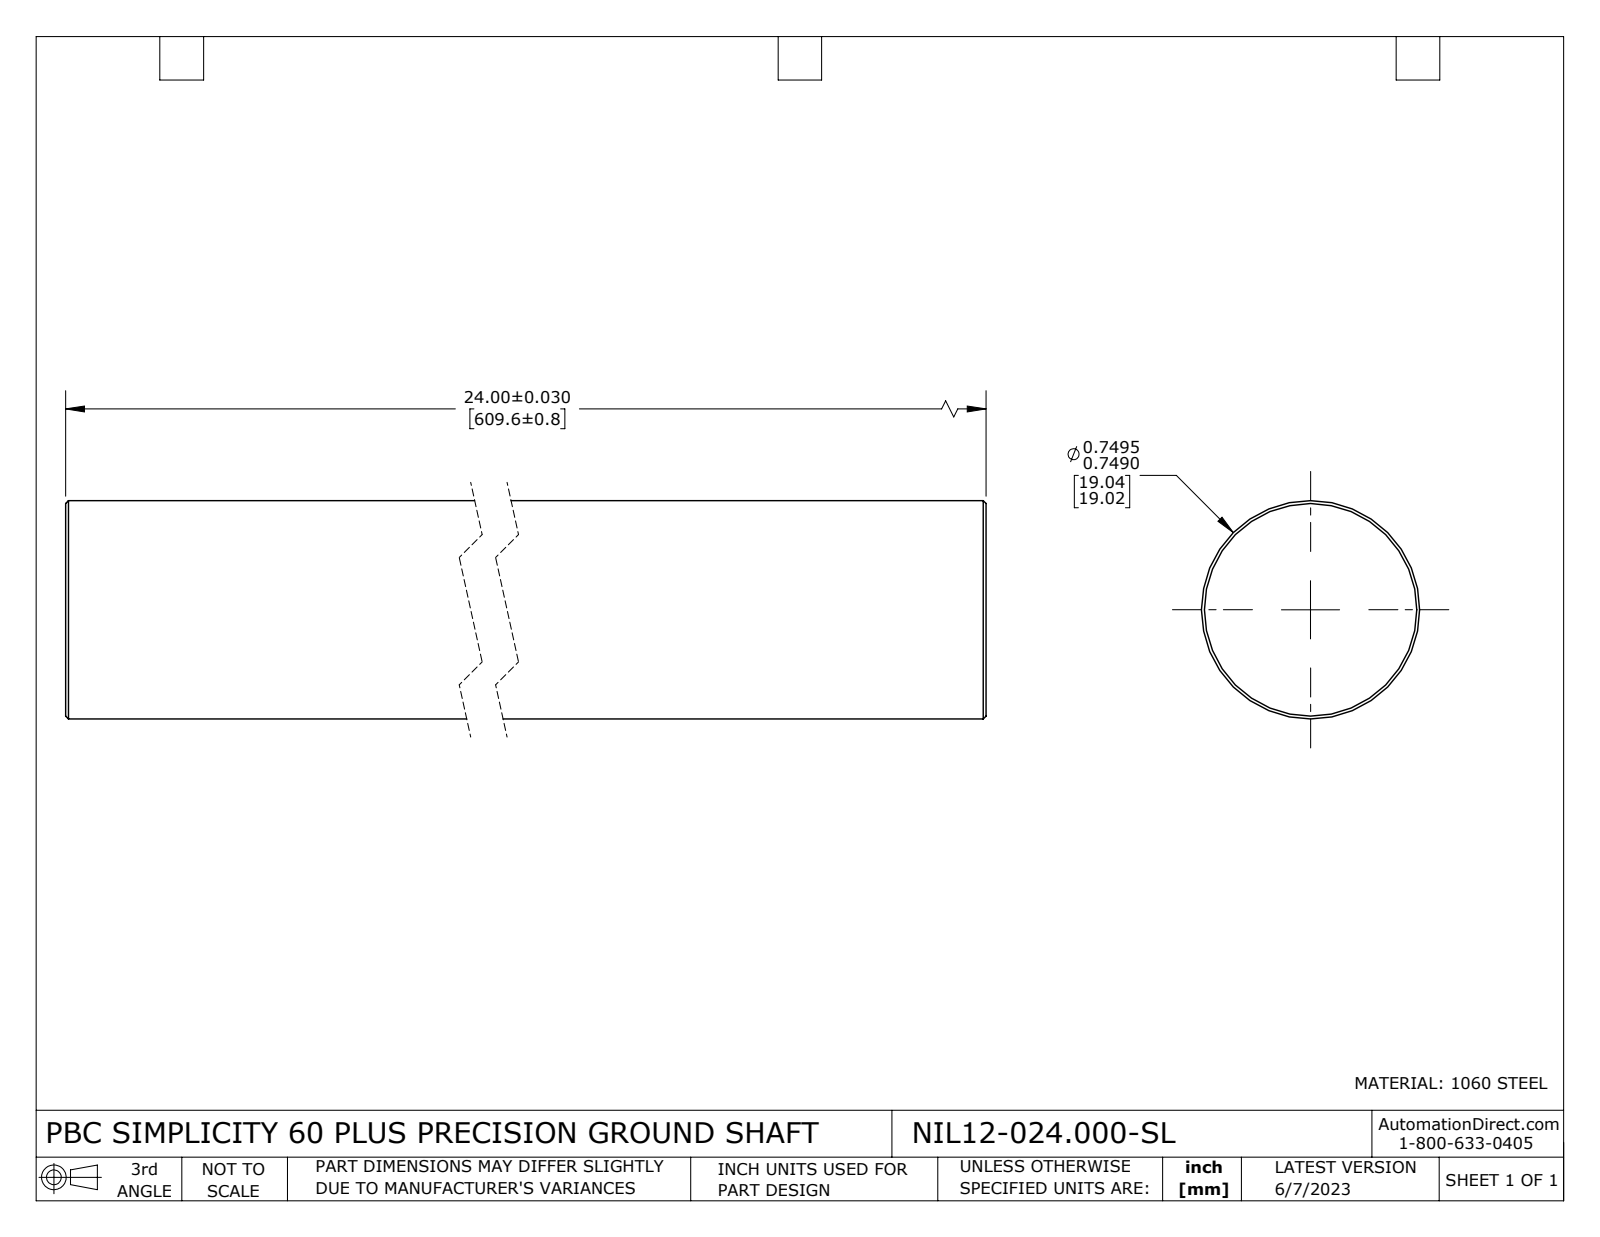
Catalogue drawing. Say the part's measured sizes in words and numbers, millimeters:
The part is named "NIL12-024.000-SL". Its 3-D file was written by "SolidWorks 2021 (CONFIG_CONTROL_DESIGN)". It is 1 solid with 8 faces: 2 planar, 2 cylindrical and 4 other. Overall it measures 609.6 by 19.1 by 19.1 millimeters. Its volume is 173 700 cubic millimeters and its surface area 37 030 square millimeters. Round bosses or shafts: 1 of diameter 19.1. The main face-to-face distances are 609.6.
